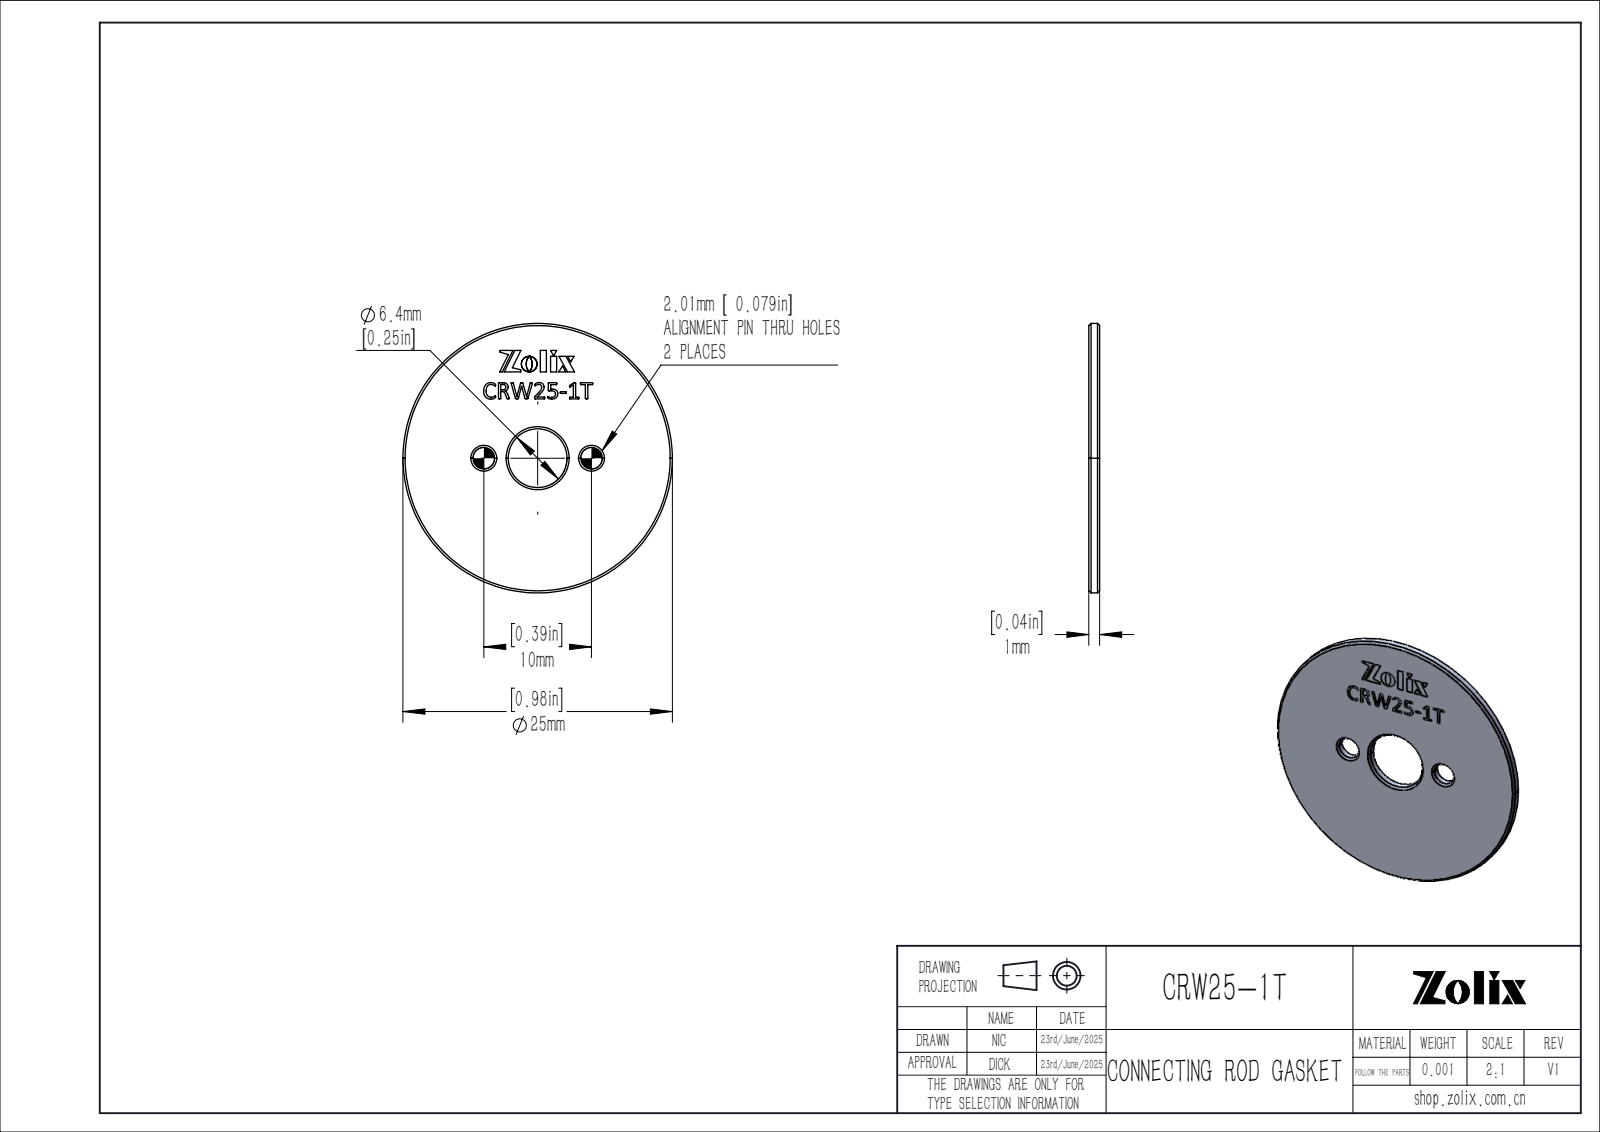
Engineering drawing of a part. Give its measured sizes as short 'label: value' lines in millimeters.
name: CRW25-1T
written by: SolidWorks 2020 (CONFIG_CONTROL_DESIGN)
unit: mm
bodies: 1 solid, 326 faces (226 planar, 8 cylindrical, 92 other)
size: 25 × 25 × 1
volume: 457 mm³; area: 1 007 mm²
holes: 2× ⌀2, 1× ⌀5.45
bosses: 1× ⌀25
face distances: 1, 0.98, 0.56, 2, 2.5, 8.07, 1.12, 6.95, 3, 1.32
hole spacings: 5, 10
